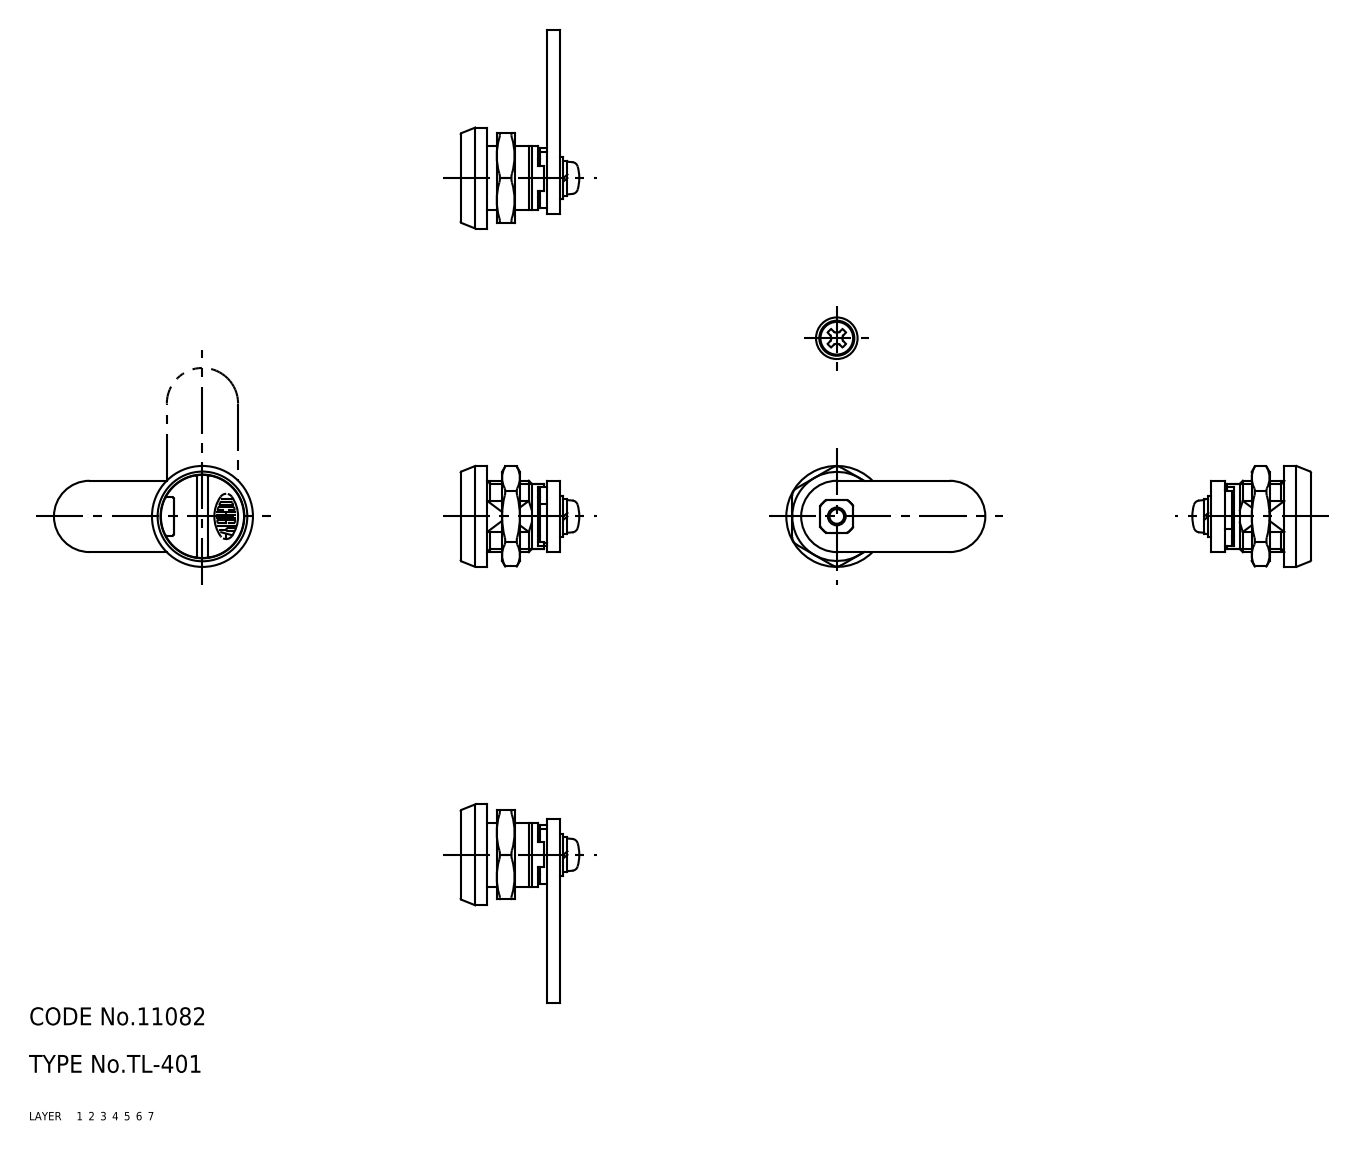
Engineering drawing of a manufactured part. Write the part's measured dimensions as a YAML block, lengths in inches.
part_name: "nut; control cam; TL_401; cam (+1 more)"
step_written_by: "SolidWorks 2015 (AUTOMOTIVE_DESIGN)"
units: inches
bodies: {solids: 4, faces: 139, planar: 78, cylindrical: 39, other: 22}
overall_size: [1.319, 0.787, 0.682]
volume: 0.178
surface_area: 4.573
round_holes:
  - {diameter: 0.118, count: 1}
  - {diameter: 0.358, count: 1}
  - {diameter: 0.555, count: 1}
round_bosses_or_shafts:
  - {diameter: 0.669, count: 1}
  - {diameter: 0.551, count: 1}
  - {diameter: 0.472, count: 1}
  - {diameter: 0.433, count: 1}
  - {diameter: 0.276, count: 1}
  - {diameter: 0.256, count: 1}
  - {diameter: 0.232, count: 1}
partial_cylinders:
  - {radius: 0.13, count: 1}
  - {radius: 0.173, count: 1}
  - {radius: 0.213, count: 1}
  - {radius: 0.236, count: 1}
face_to_face_distances: [0.091, 0.197, 0.177, 0.661, 0.571, 0.394, 0.484, 0.079, 0.118, 0.256]
